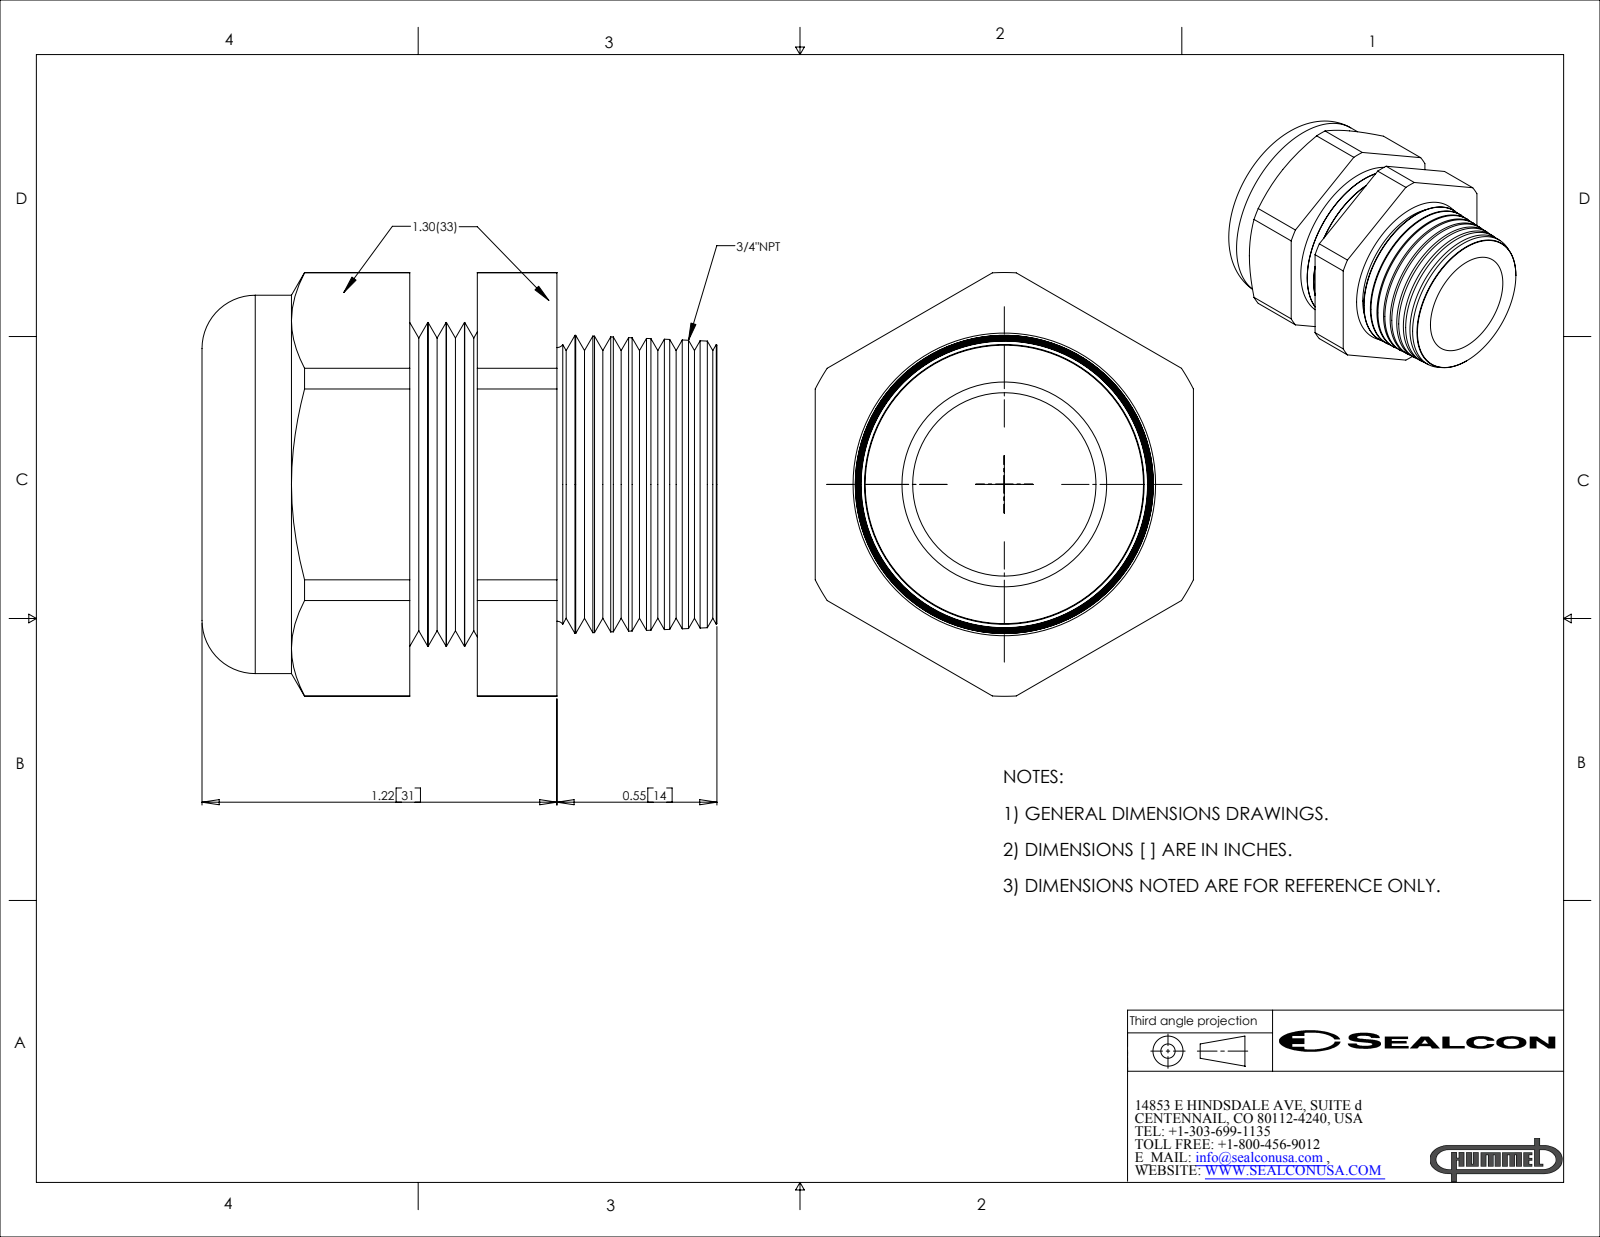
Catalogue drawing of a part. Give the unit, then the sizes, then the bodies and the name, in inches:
Units: inches
Overall size (bounding box): 1.77 × 1.456 × 1.3
Round holes (diameter × count): ⌀0.63 ×1, ⌀0.876 ×1
Round bosses / shafts (diameter × count): ⌀1.3 ×1, ⌀1.113 ×1
Partial cylindrical surfaces — rounded edges, fillets, slot ends (radius × count): R0.728 ×1
Main face-to-face distances: 1.3, 0.913, 0.407, 0.506, 0.639, 0.232, 0.274, 1.463, 1.056, 0.824
Volume: 1.379 in³ · Surface area: 17.64 in²
Bodies: 2 solids, 136 faces (20 planar, 30 cylindrical, 86 other)
Part name (STEP PRODUCT): CD21NR-GY
STEP written by: SolidWorks 2007 (CONFIG_CONTROL_DESIGN)
